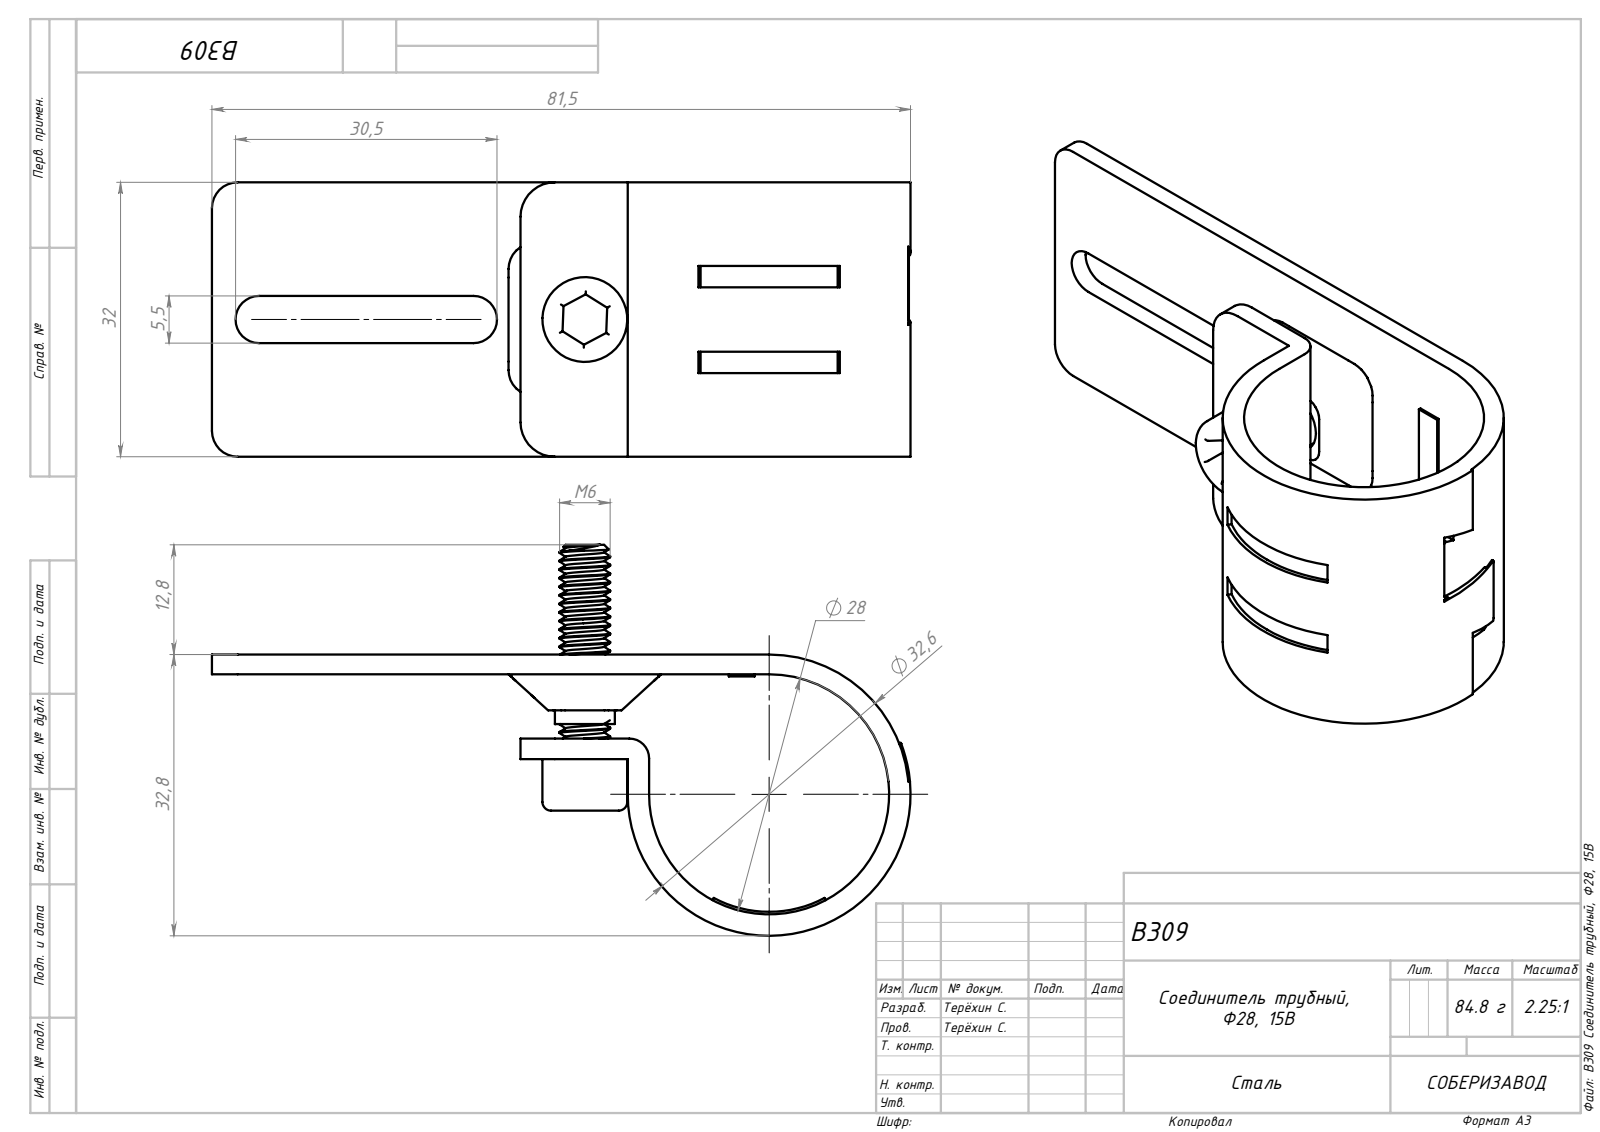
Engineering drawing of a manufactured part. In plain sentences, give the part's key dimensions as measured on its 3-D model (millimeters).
The part is named "B309 Соединитель трубный, Ф28, 15B". Its 3-D file was written by "SolidWorks 2022 (AUTOMOTIVE_DESIGN)". It is 1 solid with 248 faces: 86 planar, 93 cylindrical and 69 other. Overall it measures 81.5 by 45.6 by 32 millimeters. Its volume is 12 328 cubic millimeters and its surface area 12 124 square millimeters. Round holes: 1 of diameter 5.3, 1 of diameter 7, 1 of diameter 7.5. Round bosses or shafts: 1 of diameter 9.9, 1 of diameter 5.9. Partial cylindrical surfaces (rounded edges, fillets, slot ends): 6 of radius 0.3, 6 of radius 0.5, 6 of radius 4, 2 of radius 2.75, 2 of radius 3, 1 of radius 2.3, 1 of radius 13.7, 1 of radius 14. The main face-to-face distances are 2.3, 7.5, 9.8, 32, 9.9, 12.2, 2.4, 2.5, 13.25, 18.75.
